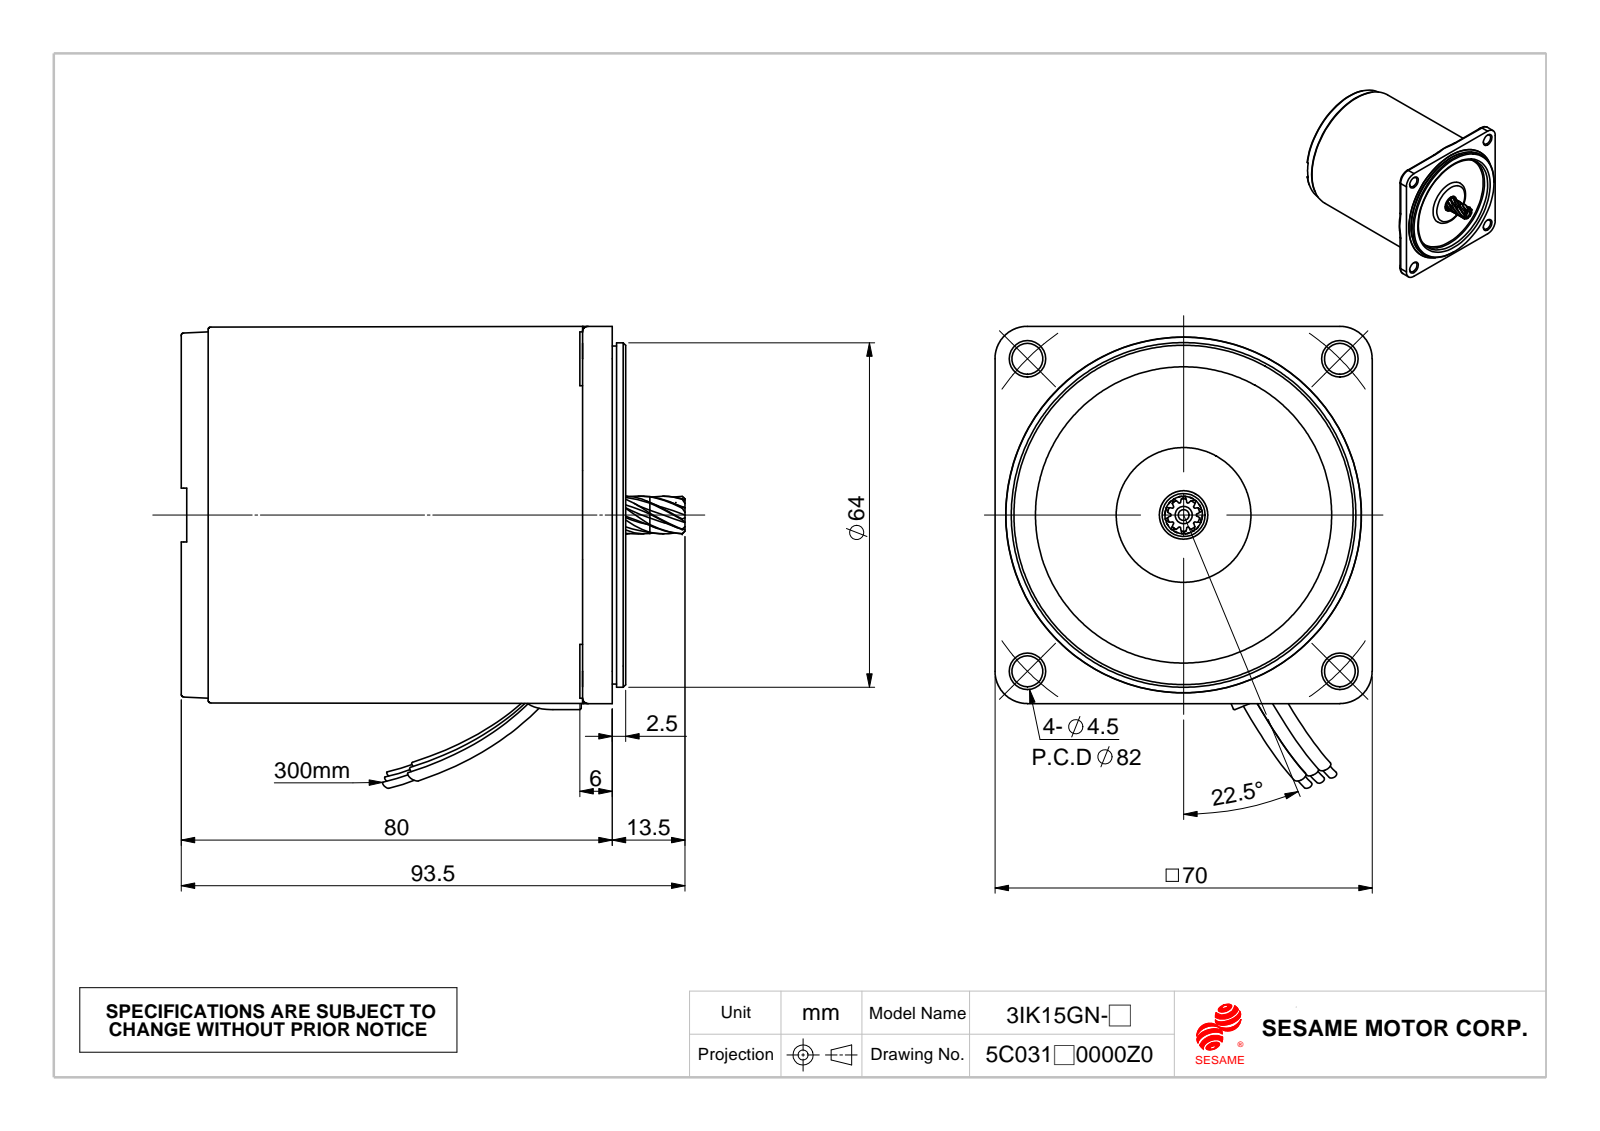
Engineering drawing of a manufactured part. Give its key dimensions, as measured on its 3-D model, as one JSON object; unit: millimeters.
{"part_name": "15GN_0.成品; M315_2車工; C364_車工(成品); 線扣", "step_written_by": "SolidWorks 2010 (CONFIG_CONTROL_DESIGN)", "units": "millimeters", "bodies": {"solids": 7, "faces": 292, "planar": 72, "cylindrical": 82, "other": 138}, "overall_size": [93.5, 85.74, 70], "volume_mm3": 311750, "surface_area_mm2": 39193, "round_holes": [[5.75, 4], [2, 1], [7.2, 1], [9, 1], [9.5, 1], [18, 1], [55, 1], [58.2, 1], [60.5, 1], [66, 1]], "round_bosses_or_shafts": [[10, 4], [63.93, 1], [62.73, 1], [57.42, 1], [57.2, 1], [9.3, 1], [8, 1], [6.99, 1]], "partial_cylinders_radius": [[0.25, 8], [1, 4], [6, 4], [5.25, 1], [33.98, 1]], "face_to_face_distances": [77.4, 77.5, 1.51, 75.89, 1.61, 1.5, 79, 3.11, 1.6, 4], "hole_center_spacings": [41.01, 58, 82.02]}
